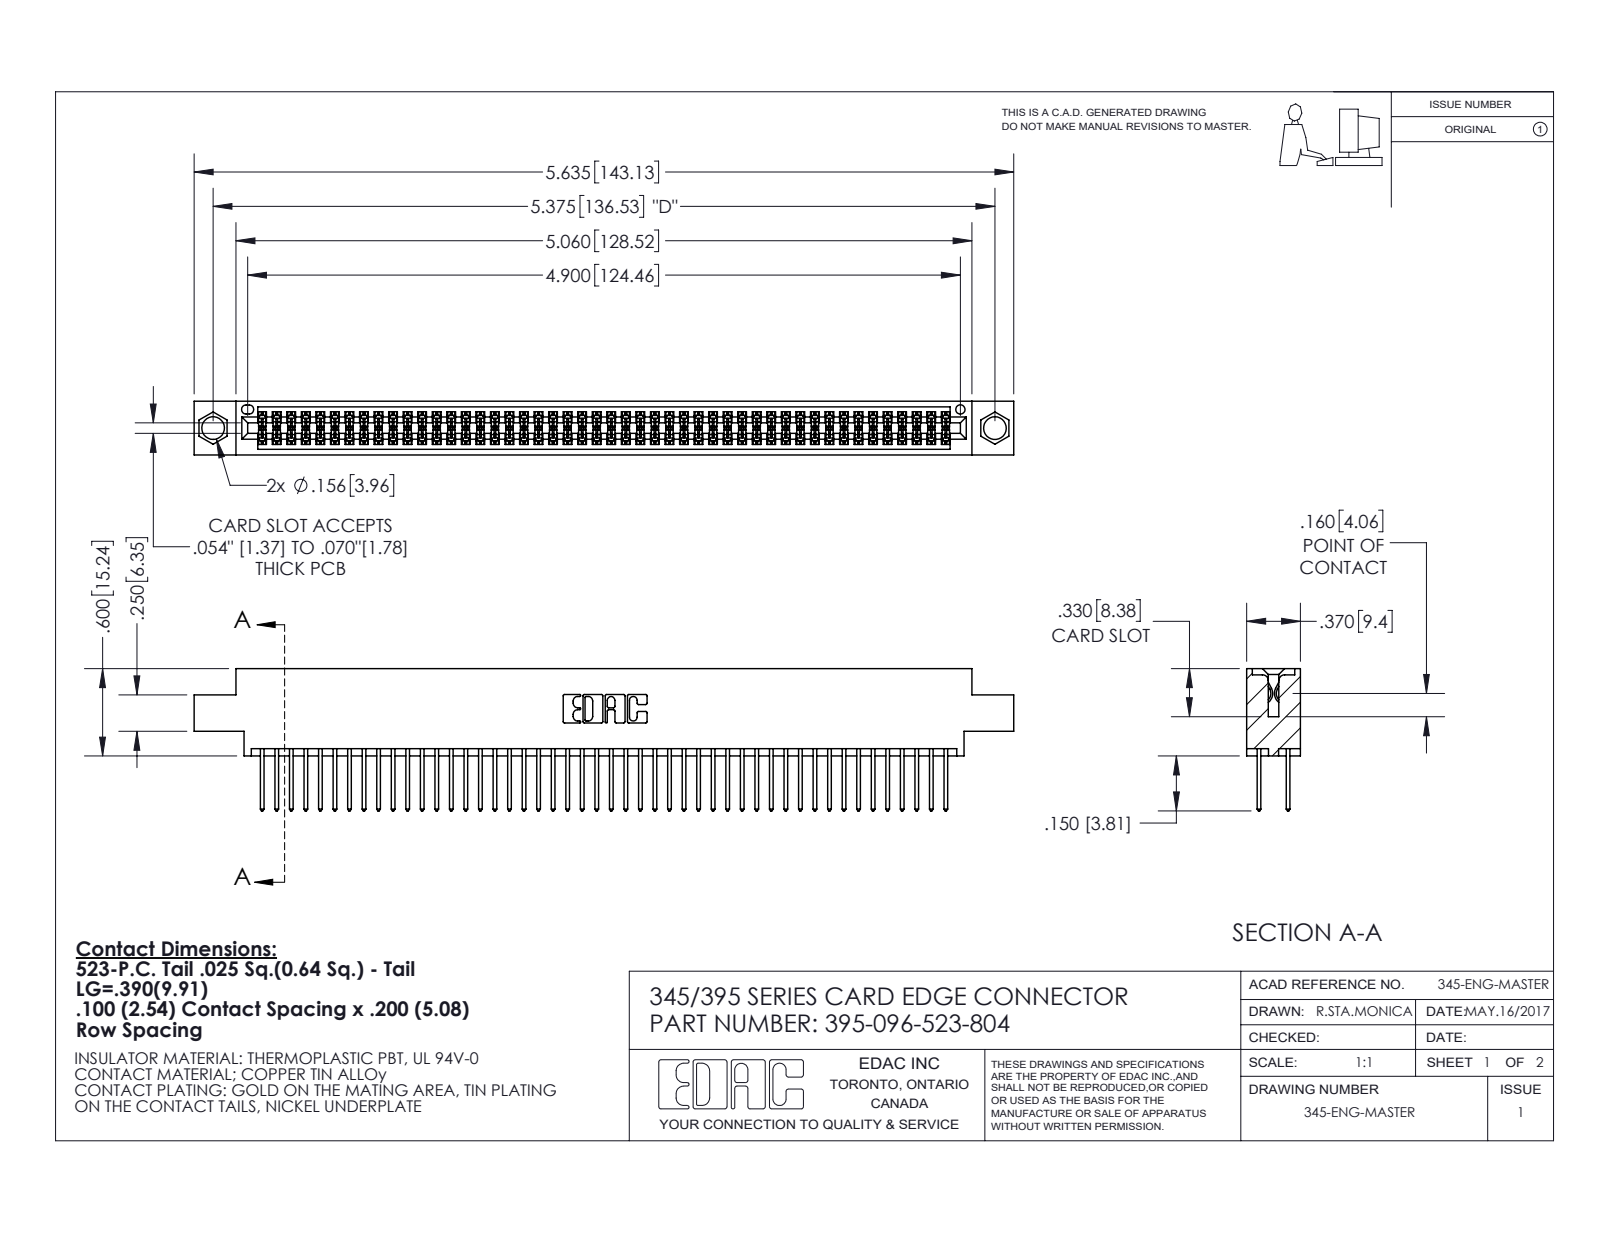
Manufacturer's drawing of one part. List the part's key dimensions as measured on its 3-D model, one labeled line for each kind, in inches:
Part name (STEP PRODUCT): 345 Part_0.170 Offset - 0.156 Dia-TI; 345-292-001_345-293-123; 395-096-523-804
STEP written by: SolidWorks 2020 (CONFIG_CONTROL_DESIGN)
Units: inches
Bodies: 97 solids, 4944 faces (3266 planar, 1678 cylindrical, 0 other)
Overall size (bounding box): 5.635 × 0.977 × 0.37
Volume: 0.85 in³ · Surface area: 33.47 in²
Round holes (diameter × count): ⌀0.156 ×2, ⌀0.064 ×1
Partial cylindrical surfaces — rounded edges, fillets, slot ends (radius × count): R0.006 ×192, R0.01 ×96, R0.01 ×22, R0.007 ×6, R0.031 ×6, R0.026 ×3, R0.014 ×2, R0.019 ×2
Main face-to-face distances: 0.072, 0.298, 0.2, 0.098, 0.272, 0.025, 0.37, 0.225, 0.175, 0.149
Hole centre spacings: 0.27, 5.139, 5.375
